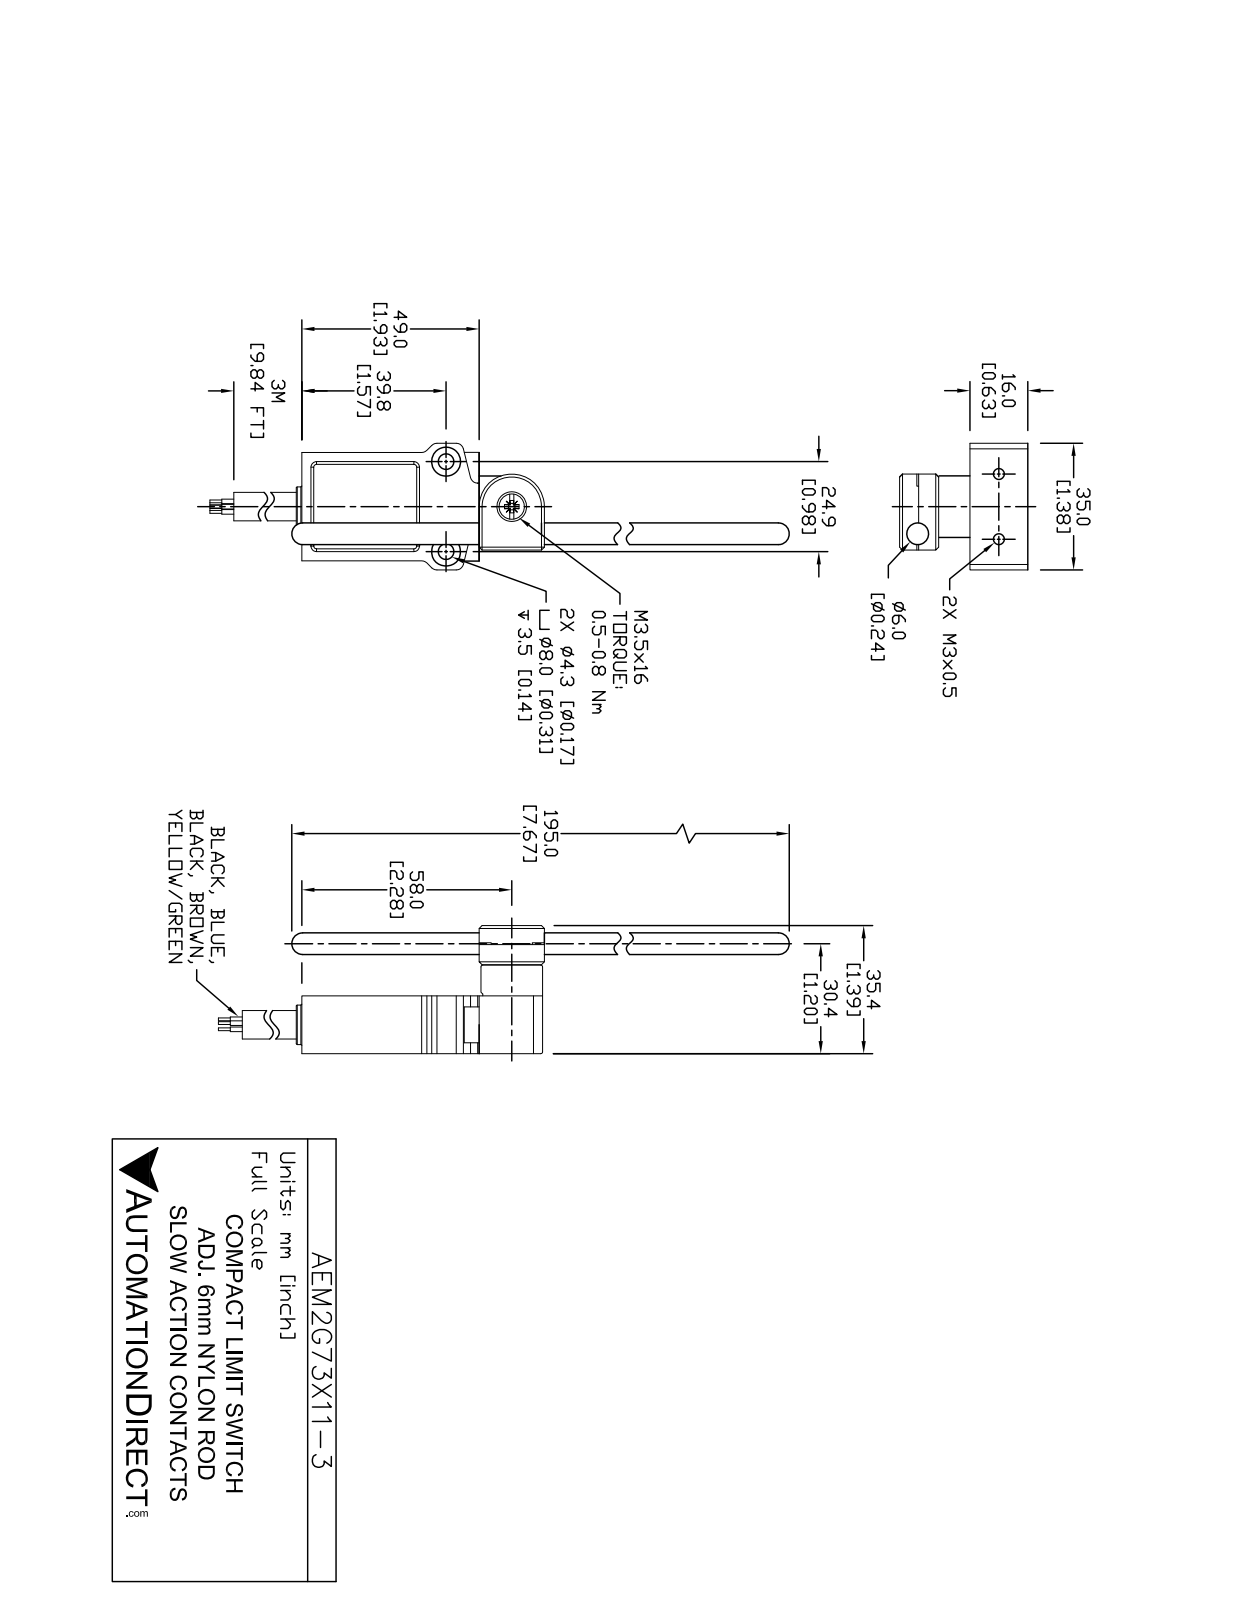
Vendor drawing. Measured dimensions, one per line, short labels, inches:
name: AEM2G73X11-3_Default
written by: SolidWorks 2021 (CONFIG_CONTROL_DESIGN)
unit: in
bodies: 3 solids, 134 faces (82 planar, 42 cylindrical, 10 other)
size: 8.178 × 1.414 × 1.378
volume: 2.245 in³; area: 21.65 in²
holes: 2× ⌀0.118, 2× ⌀0.173, 2× ⌀0.323, 1× ⌀0.197, 1× ⌀0.32
bosses: 1× ⌀0.622, 1× ⌀0.289, 1× ⌀0.276, 1× ⌀0.24
rounds: 8× R0.079, 1× R0.256, 1× R0.355
face distances: 0.63, 1.181, 0.354, 0.215, 1.929, 0.984, 0.28, 0.902, 0.472, 0.43
hole spacings: 0.863, 0.748, 0.984
